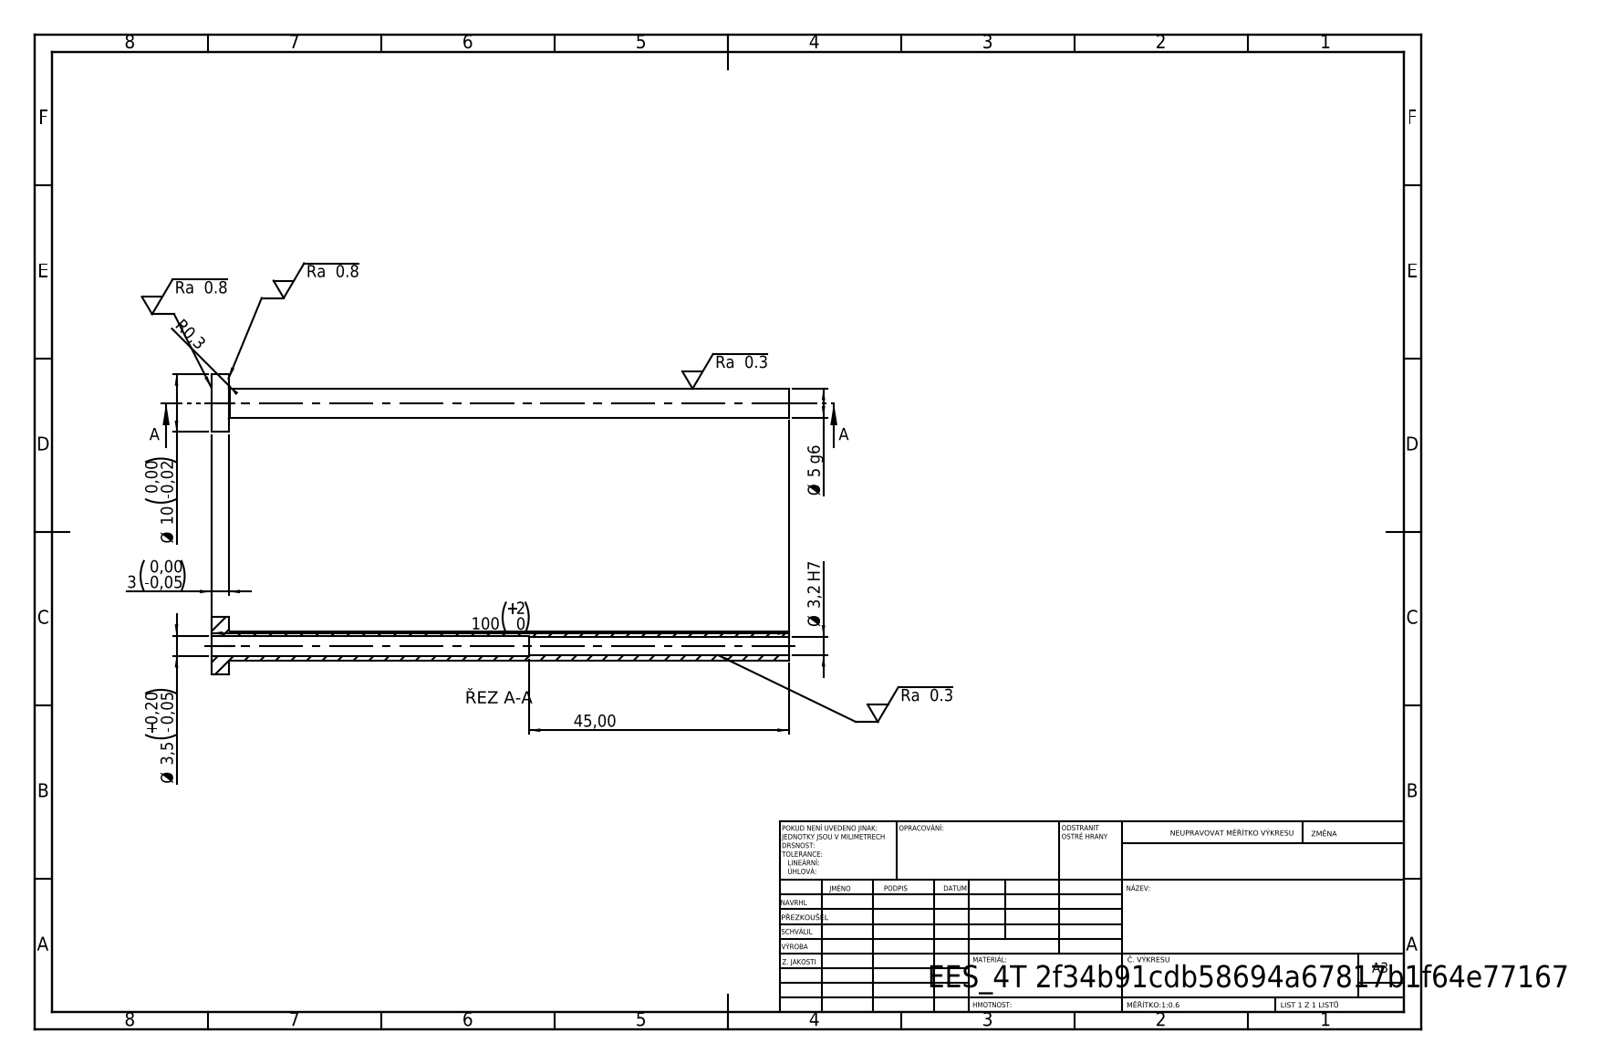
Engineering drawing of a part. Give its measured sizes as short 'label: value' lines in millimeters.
written by: SolidWorks 2019 (CONFIG_CONTROL_DESIGN)
unit: mm
bodies: 1 solid, 14 faces (4 planar, 8 cylindrical, 2 other)
size: 100 × 10 × 10
volume: 1 249 mm³; area: 2 814 mm²
holes: 1× ⌀3.2, 1× ⌀3.5
bosses: 1× ⌀10, 1× ⌀5
face distances: 3, 100, 97, 55, 52, 45
